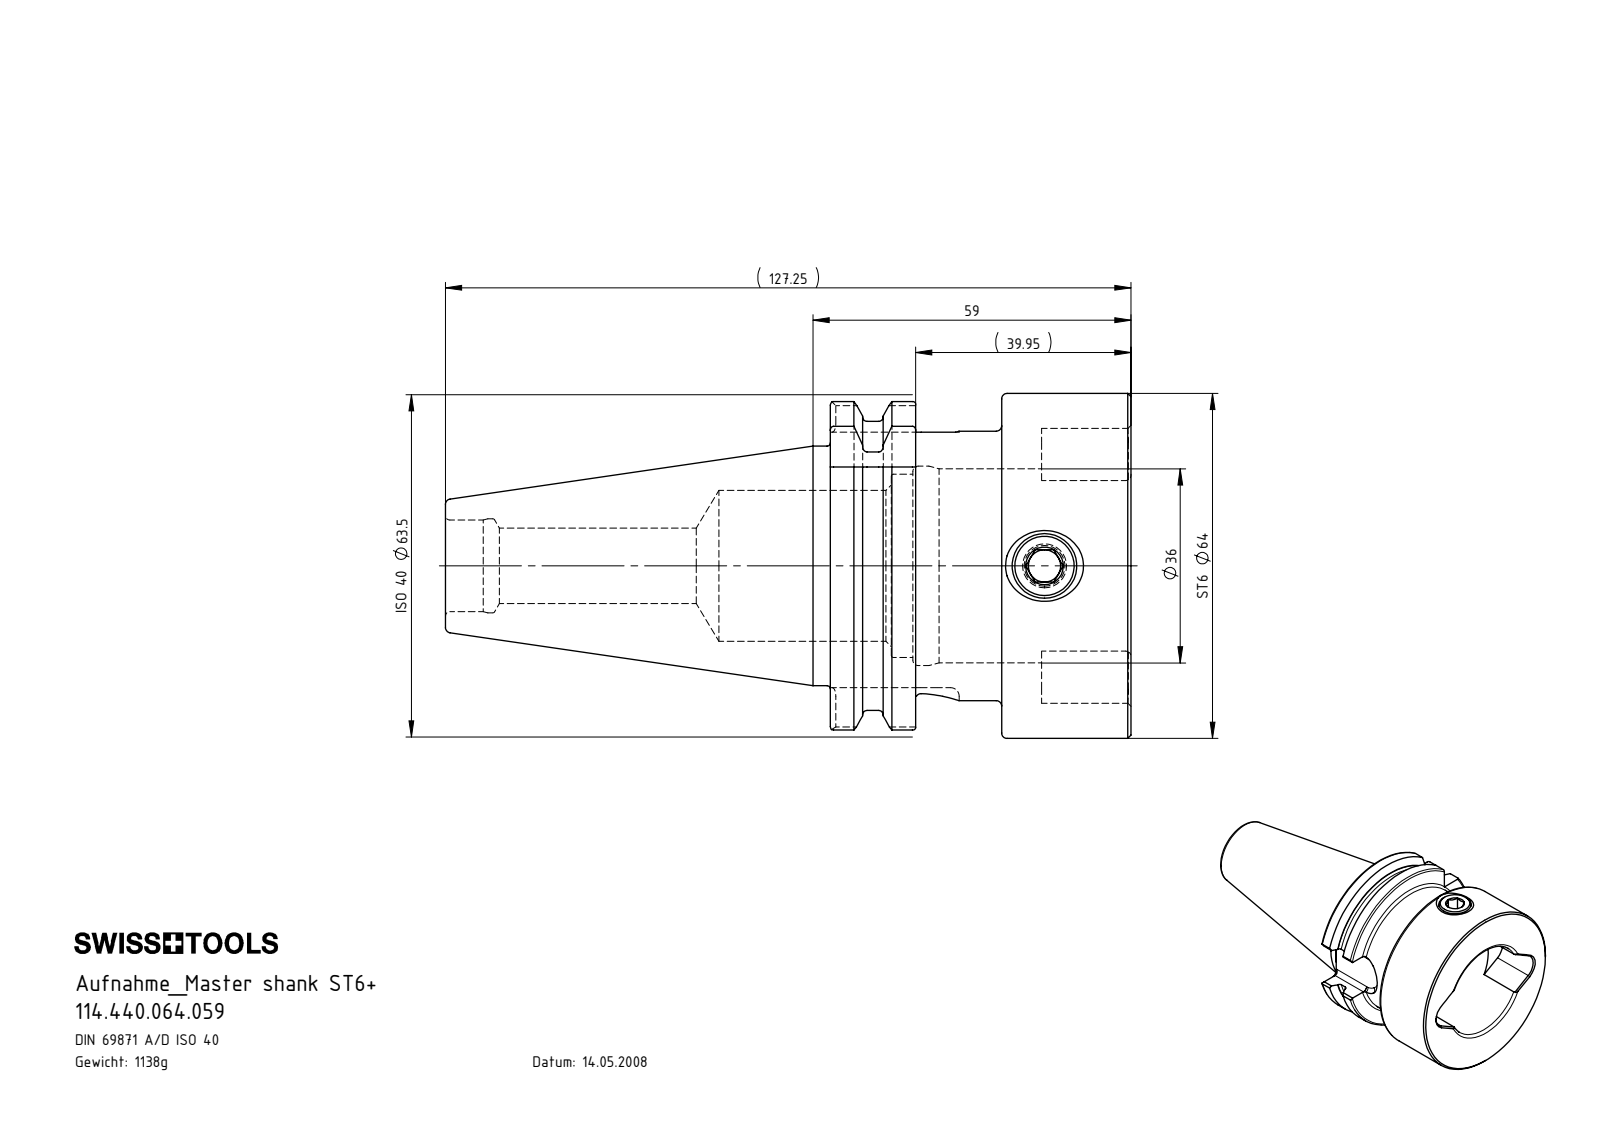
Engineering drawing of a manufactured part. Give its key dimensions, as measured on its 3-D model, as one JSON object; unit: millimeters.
{"part_name": "SK4-ST6.K01.059; ST6-ER1.001.018_A; SK4-ST6.K01.059_A", "step_written_by": "SolidWorks 2015 (CONFIG_CONTROL_DESIGN)", "units": "millimeters", "bodies": {"solids": 2, "faces": 178, "planar": 52, "cylindrical": 50, "other": 76}, "overall_size": [127.25, 64, 64], "volume_mm3": 145016, "surface_area_mm2": 37259, "round_holes": [[11, 1], [14, 1], [17, 1], [17.45, 1], [28, 1], [34, 1], [36, 1], [37, 1]], "round_bosses_or_shafts": [[64, 1], [50, 1], [44.45, 1], [12, 1]], "partial_cylinders_radius": [[1.6, 8], [5.2, 2], [8, 1], [8.05, 1], [28, 1], [31.75, 1]], "face_to_face_distances": [55.8, 31.8, 24, 15.85, 15.95, 39.95, 30.7, 47.4, 39.2, 23.35]}
